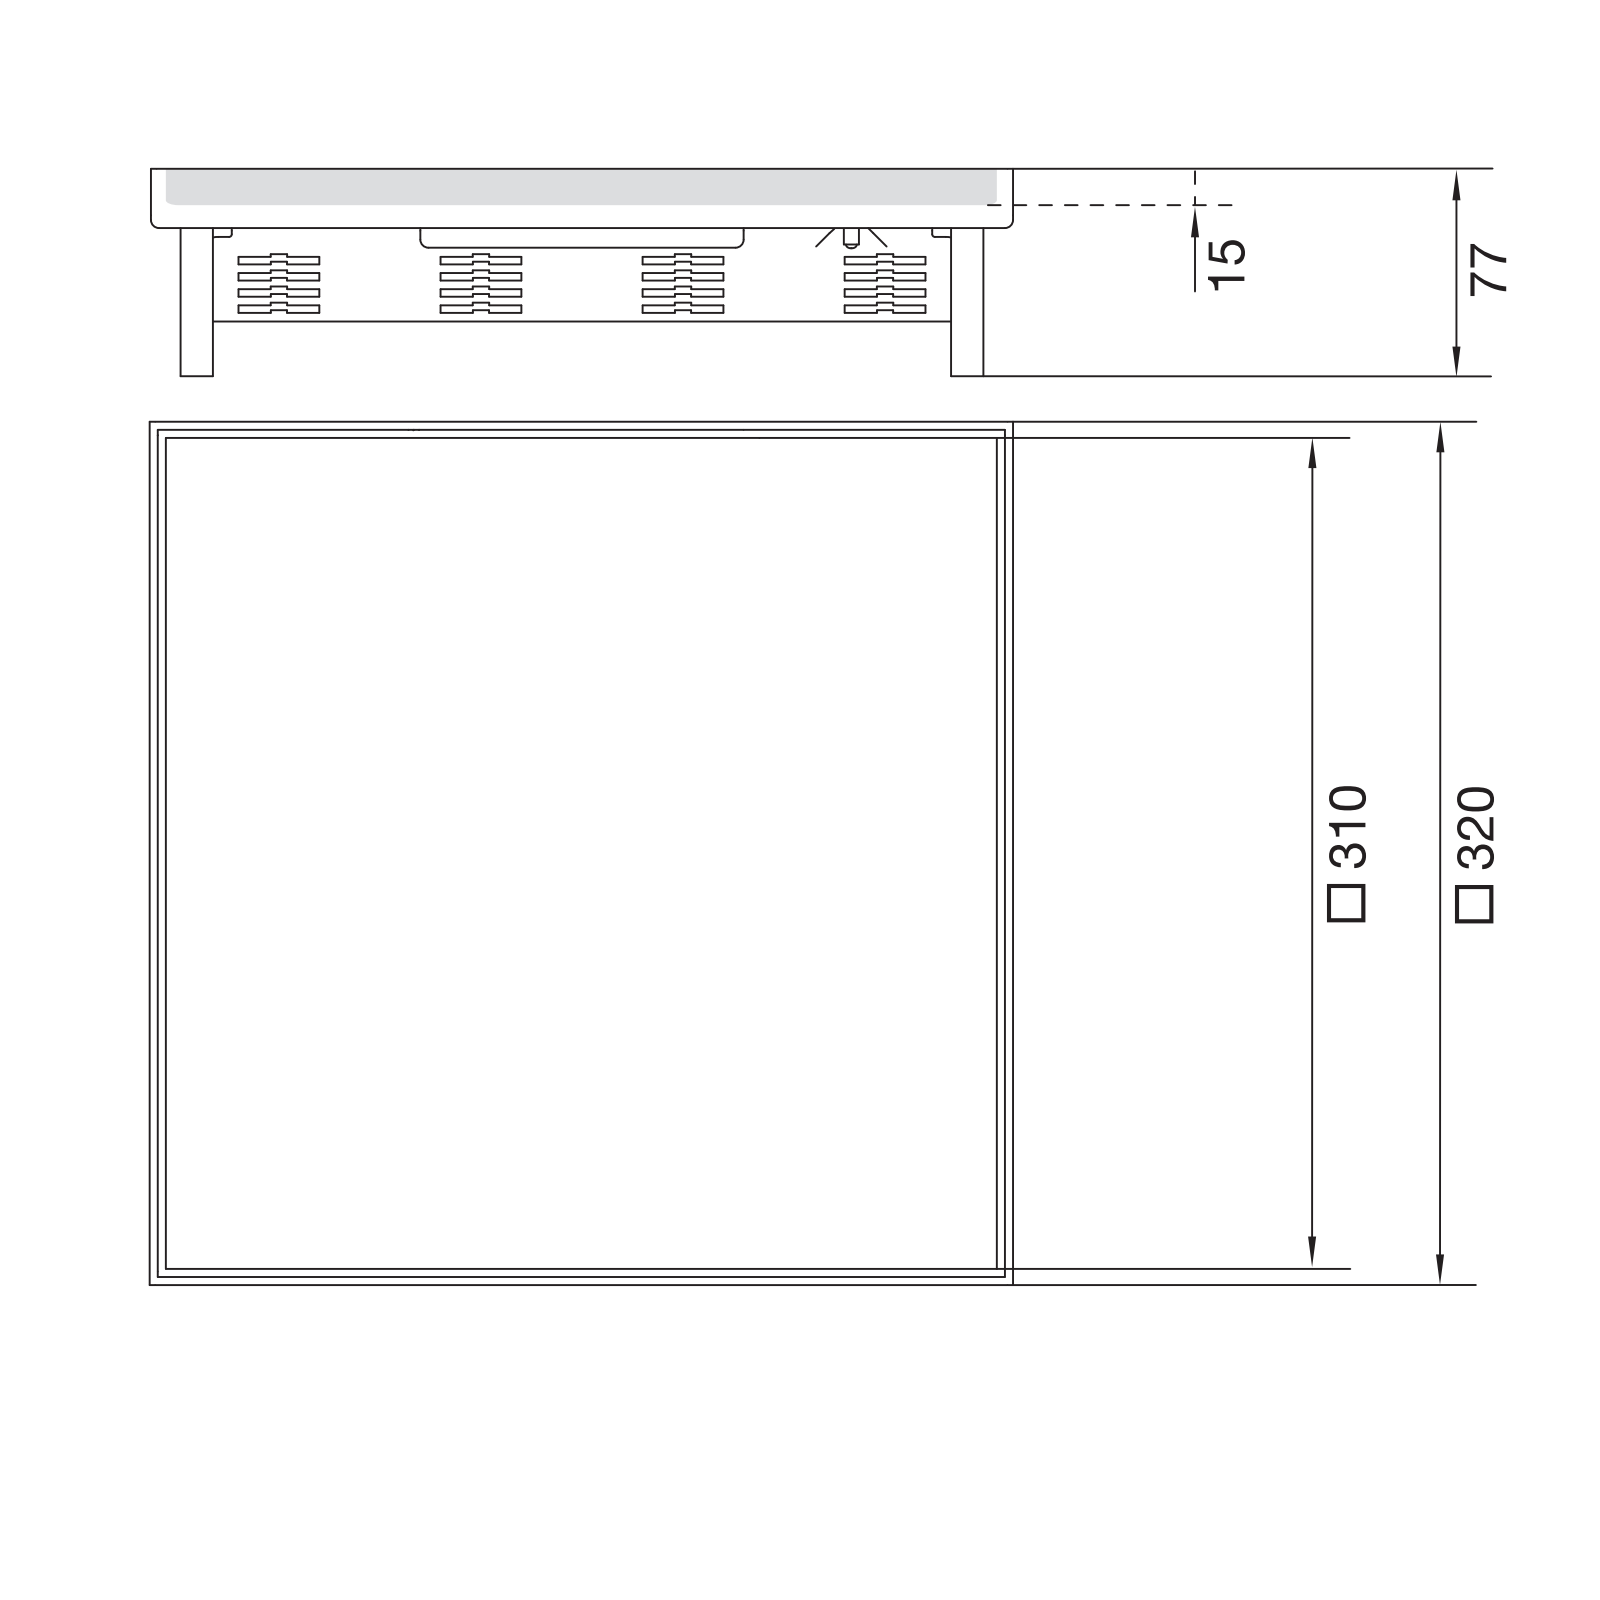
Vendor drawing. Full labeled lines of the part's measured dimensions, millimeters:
Part name (STEP PRODUCT): T-00644; U09001; T-00833_ASM; T-00649 (+2 more)
STEP written by: CREO PARAMETRIC BY PTC INC, 2022024 (AUTOMOTIVE_DESIGN)
Units: millimetres
Bodies: 2 solids, 188 faces (136 planar, 52 cylindrical, 0 other)
Overall size (bounding box): 320 × 320 × 77
Volume: 375 136 mm³ · Surface area: 394 189 mm²
Round bosses / shafts (diameter × count): ⌀12 ×4, ⌀9.85 ×4
Partial cylindrical surfaces — rounded edges, fillets, slot ends (radius × count): R1 ×10, R3 ×10, R10 ×6, R5 ×2
Main face-to-face distances: 2, 5, 3, 315, 7, 318, 45.3, 272.7, 1, 227.4
